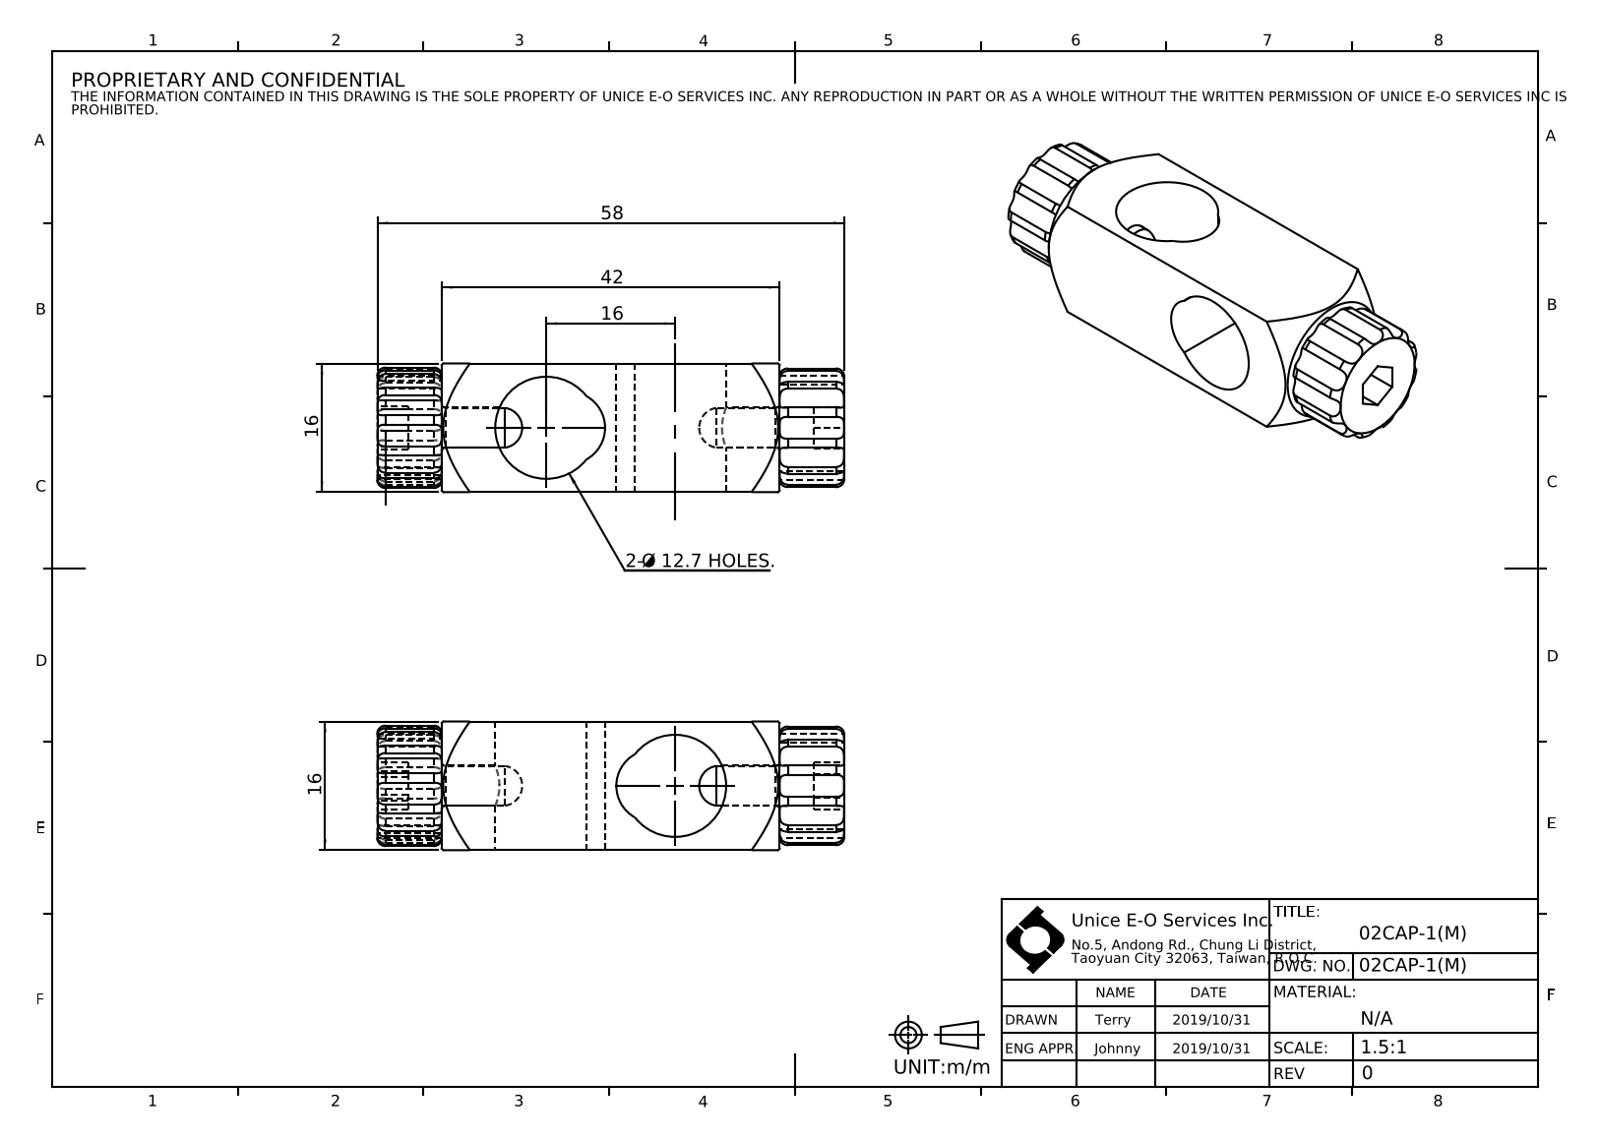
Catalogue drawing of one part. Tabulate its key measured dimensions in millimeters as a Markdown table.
| quantity | value |
| --- | --- |
| part name | 02CAP-1(M) |
| STEP written by | SolidWorks 2016 (CONFIG_CONTROL_DESIGN) |
| units | millimeters |
| bodies | 3 solids, 157 faces (24 planar, 73 cylindrical, 60 other) |
| overall size | 58 × 16 × 16 |
| volume | 8 744 mm³ |
| surface area | 5 852 mm² |
| round holes (diameter × count) | 5 × 1 |
| round bosses / shafts (diameter × count) | 4.94 × 1 |
| partial cylindrical surfaces (radius × count) | 1.5 × 24, 4.5 × 2, 6.35 × 2, 7.5 × 1 |
| main face-to-face distances | 16, 42, 8, 50, 58, 5.1, 3.8, 54.2, 4.2, 46.2 |
